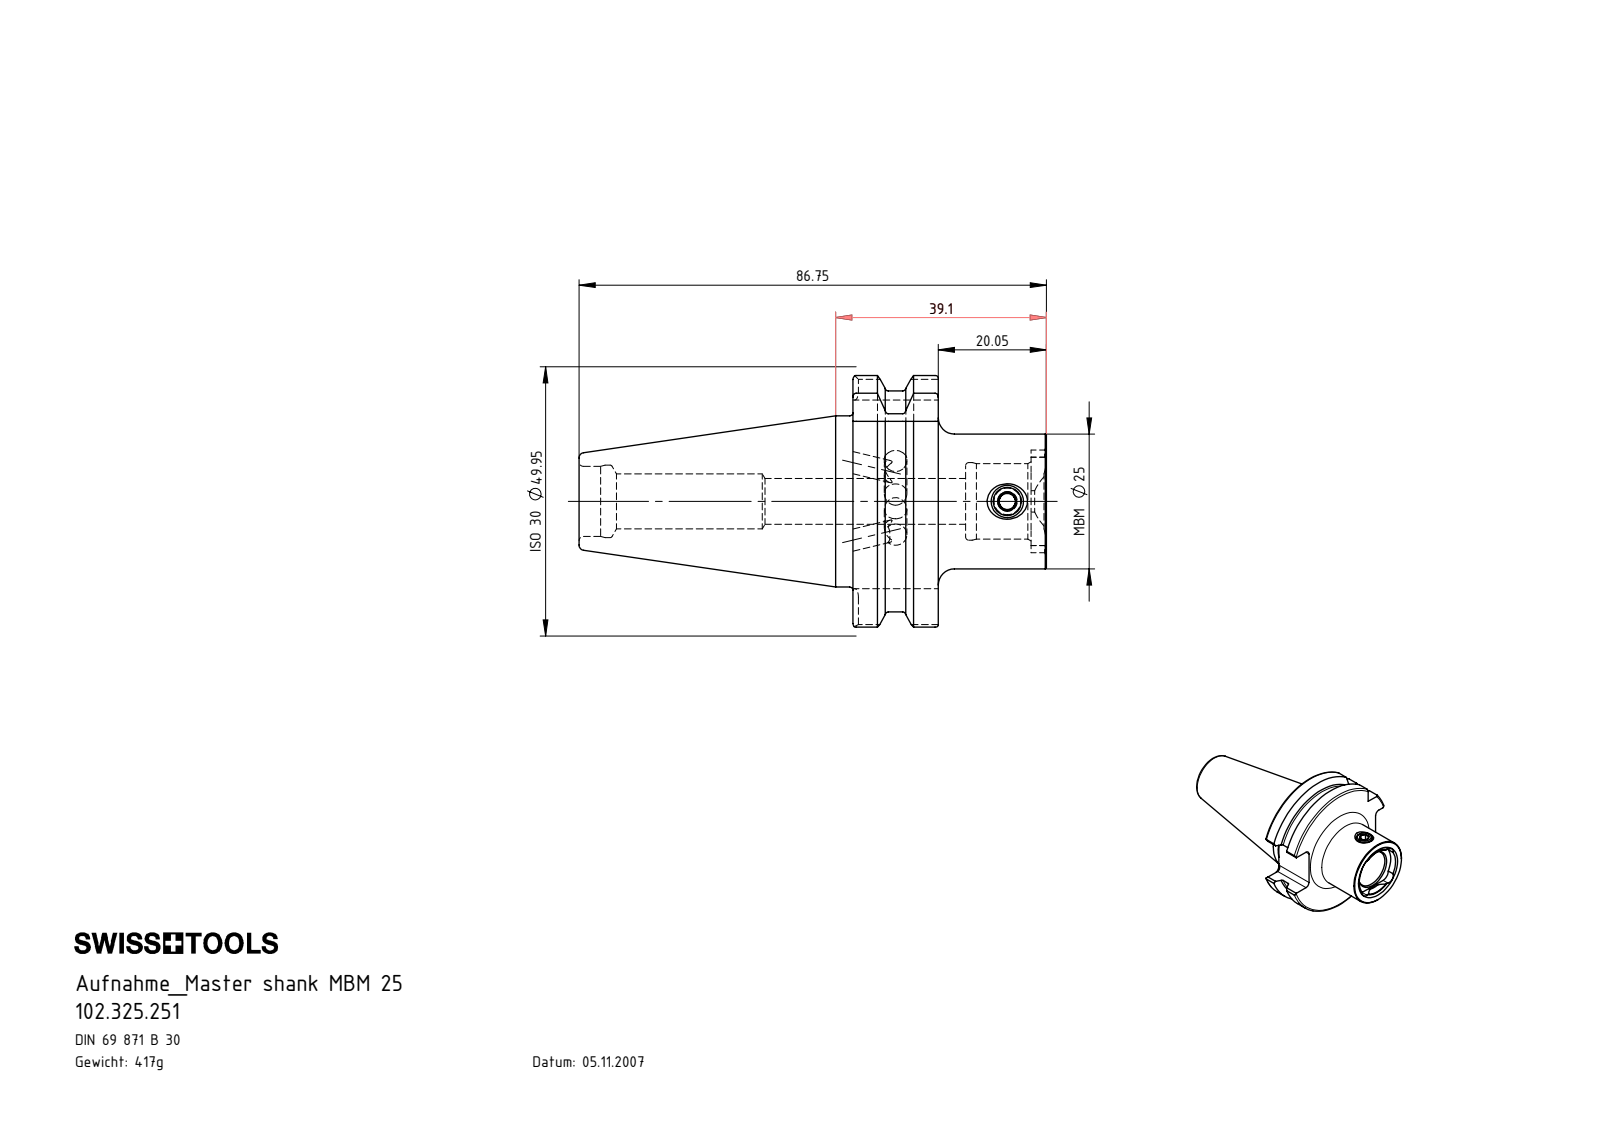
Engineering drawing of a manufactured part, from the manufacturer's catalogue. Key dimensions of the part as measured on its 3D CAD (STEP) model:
Part name (STEP PRODUCT): 102.325.251; MB2-ER1.001.008_A; SB3-MB2.K01.039_C_mit Bundkhlung
STEP written by: SolidWorks 2017 (CONFIG_CONTROL_DESIGN)
Units: millimetres
Bodies: 2 solids, 176 faces (47 planar, 59 cylindrical, 70 other)
Overall size (bounding box): 86.75 × 49.95 × 46.69
Volume: 53 168 mm³ · Surface area: 14 816 mm²
Round holes (diameter × count): ⌀4 ×2, ⌀3 ×1, ⌀4.2 ×1, ⌀5.25 ×1, ⌀8.5 ×1, ⌀10.2 ×1, ⌀13 ×1, ⌀13.45 ×1, ⌀14 ×1, ⌀14.4 ×1
Round bosses / shafts (diameter × count): ⌀31.75 ×1, ⌀25 ×1, ⌀6 ×1
Partial cylindrical surfaces — rounded edges, fillets, slot ends (radius × count): R1.6 ×8, R2.7 ×4, R8 ×1, R9.53 ×1, R22.02 ×1, R24.98 ×1
Main face-to-face distances: 15.85, 35, 35.9, 20.05, 33.05, 17.2, 2.85, 16.1, 20.9, 5.05
